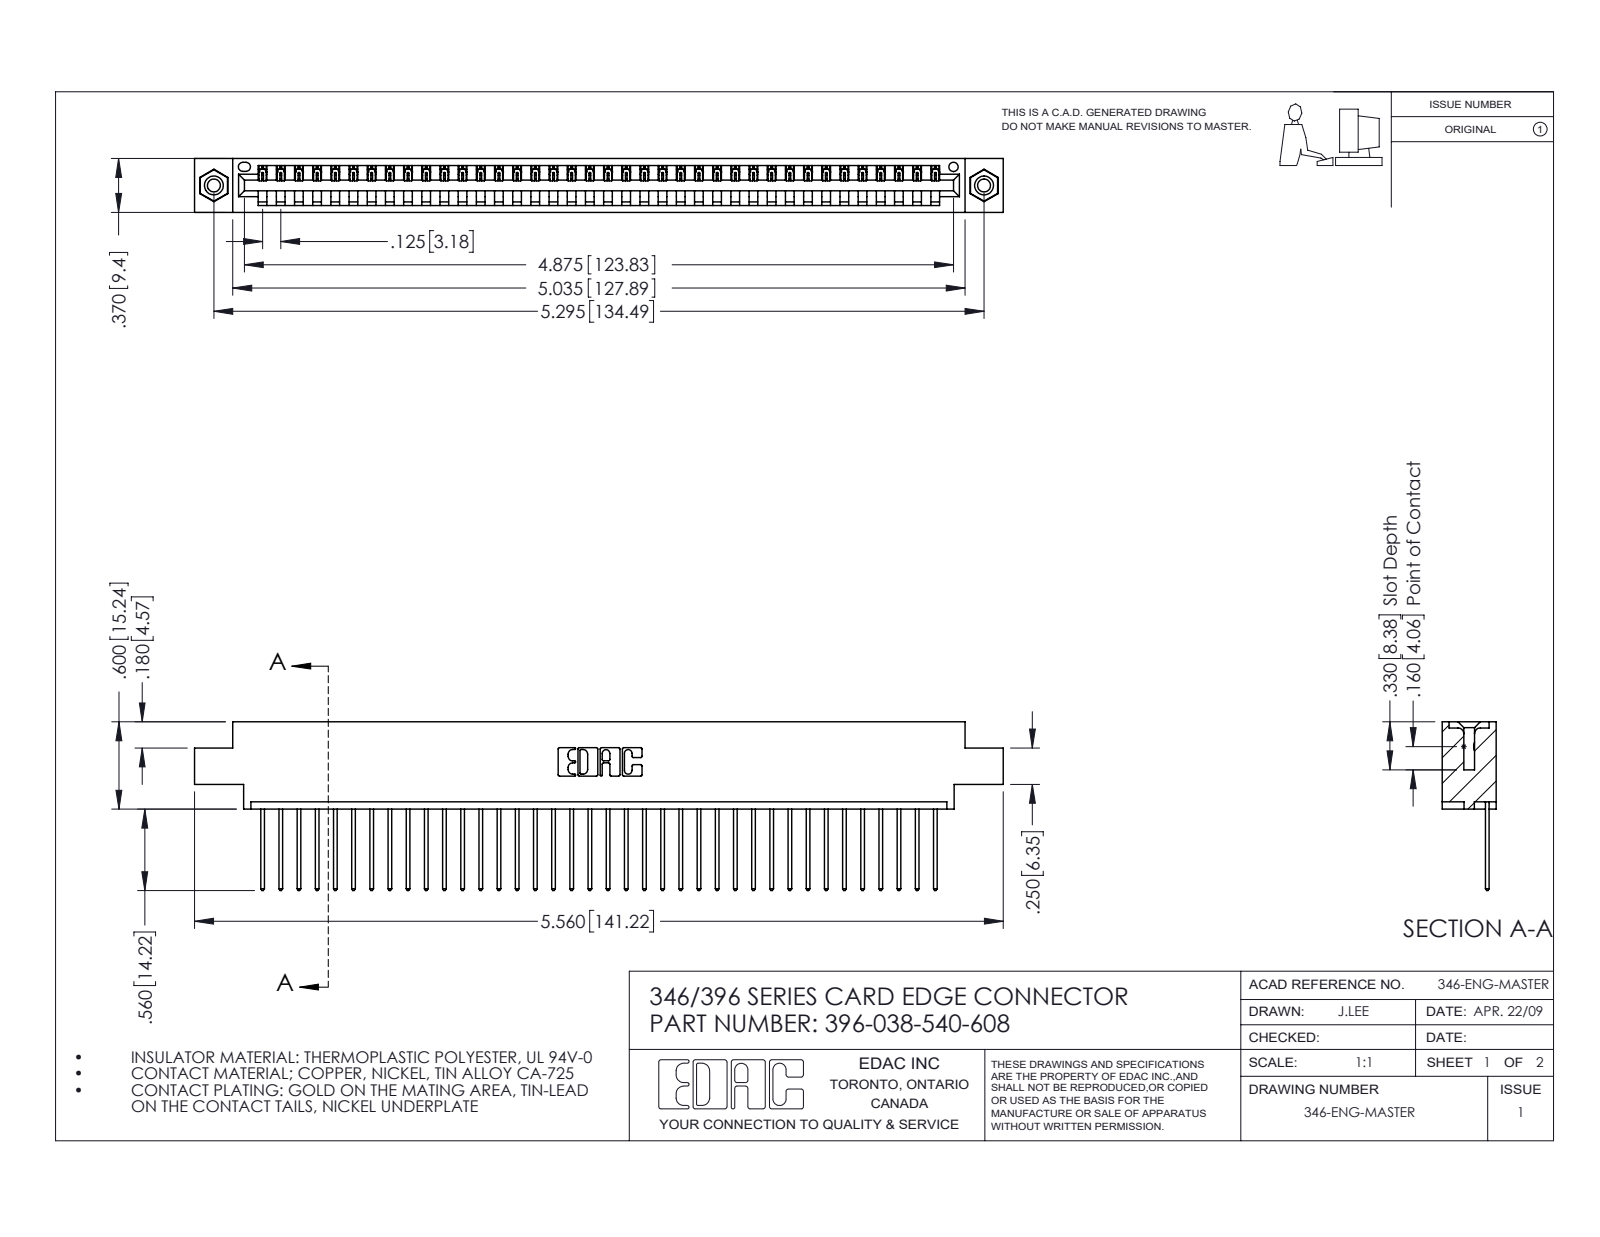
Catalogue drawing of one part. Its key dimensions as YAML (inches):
part_name: "396-038-540-608; 345-292-001_345-293-140; 345-250-001_345-250-003-102; 346 Part_0.170 Offset - 0.156 Dia-TI"
step_written_by: "SolidWorks 2016 (CONFIG_CONTROL_DESIGN)"
units: inches
bodies: {solids: 41, faces: 2390, planar: 1632, cylindrical: 742, other: 16}
overall_size: [5.56, 1.16, 0.37]
volume: 0.817
surface_area: 26.72
round_holes:
  - {diameter: 0.089, count: 2}
  - {diameter: 0.125, count: 2}
  - {diameter: 0.156, count: 2}
  - {diameter: 0.064, count: 1}
round_bosses_or_shafts:
  - {diameter: 0.155, count: 2}
partial_cylinders:
  - {radius: 0.006, count: 76}
  - {radius: 0.01, count: 76}
  - {radius: 0.01, count: 22}
  - {radius: 0.007, count: 6}
  - {radius: 0.031, count: 6}
  - {radius: 0.026, count: 3}
  - {radius: 0.031, count: 2}
  - {radius: 0.04, count: 2}
face_to_face_distances: [0.048, 0.322, 0.37, 0.25, 0.072, 0.298, 0.025, 0.222, 0.148, 0.1]
hole_center_spacings: [0.246, 5.086, 5.295]
